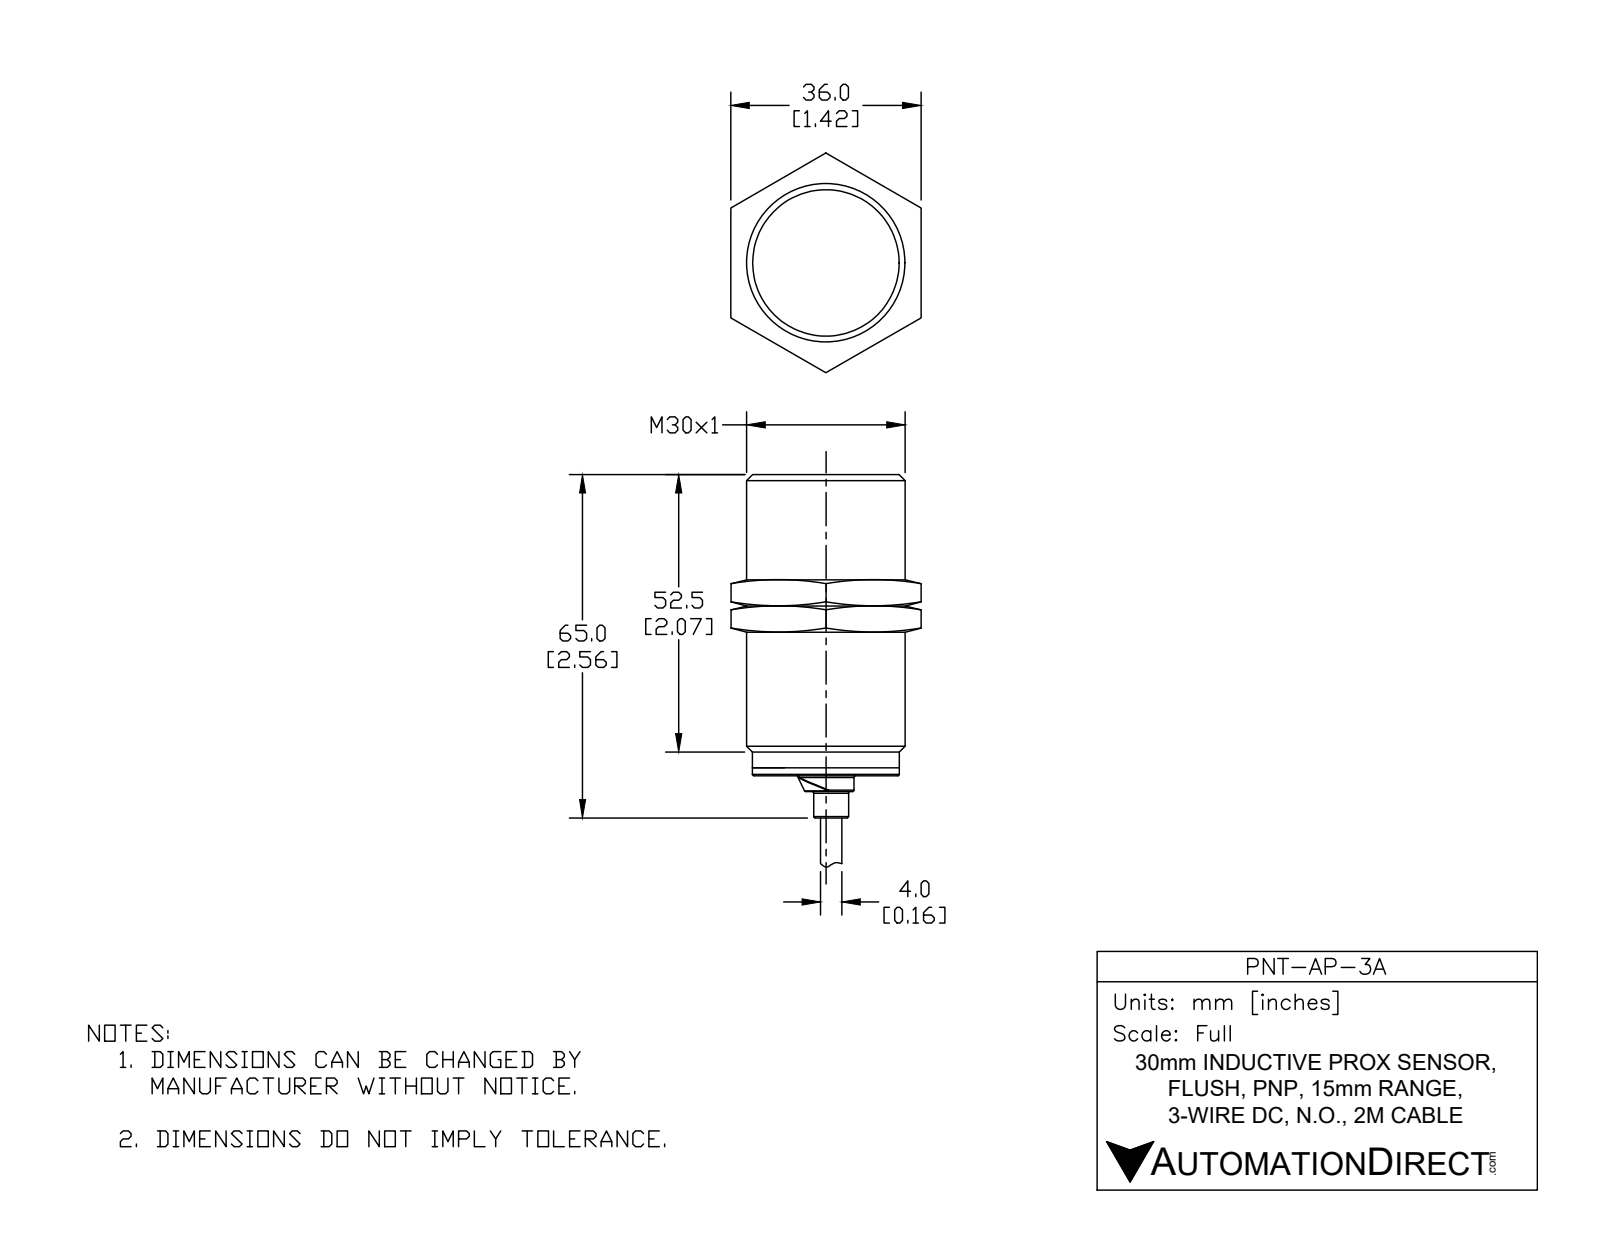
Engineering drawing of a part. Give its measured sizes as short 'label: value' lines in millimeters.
name: PNT-AP-3A
written by: SolidWorks 2017 (AUTOMOTIVE_DESIGN)
unit: mm
bodies: 1 solid, 74 faces (14 planar, 30 cylindrical, 30 other)
size: 115.8 × 30 × 30
volume: 40 750 mm³; area: 7 677 mm²
holes: 1× ⌀4.1
bosses: 6× ⌀1.2, 1× ⌀30, 1× ⌀27.8, 1× ⌀27.8, 1× ⌀10.6, 1× ⌀6.6, 1× ⌀4
rounds: 1× R2
face distances: 57, 60, 3, 57.9, 65, 8, 5, 115.8, 58.8, 55.8
